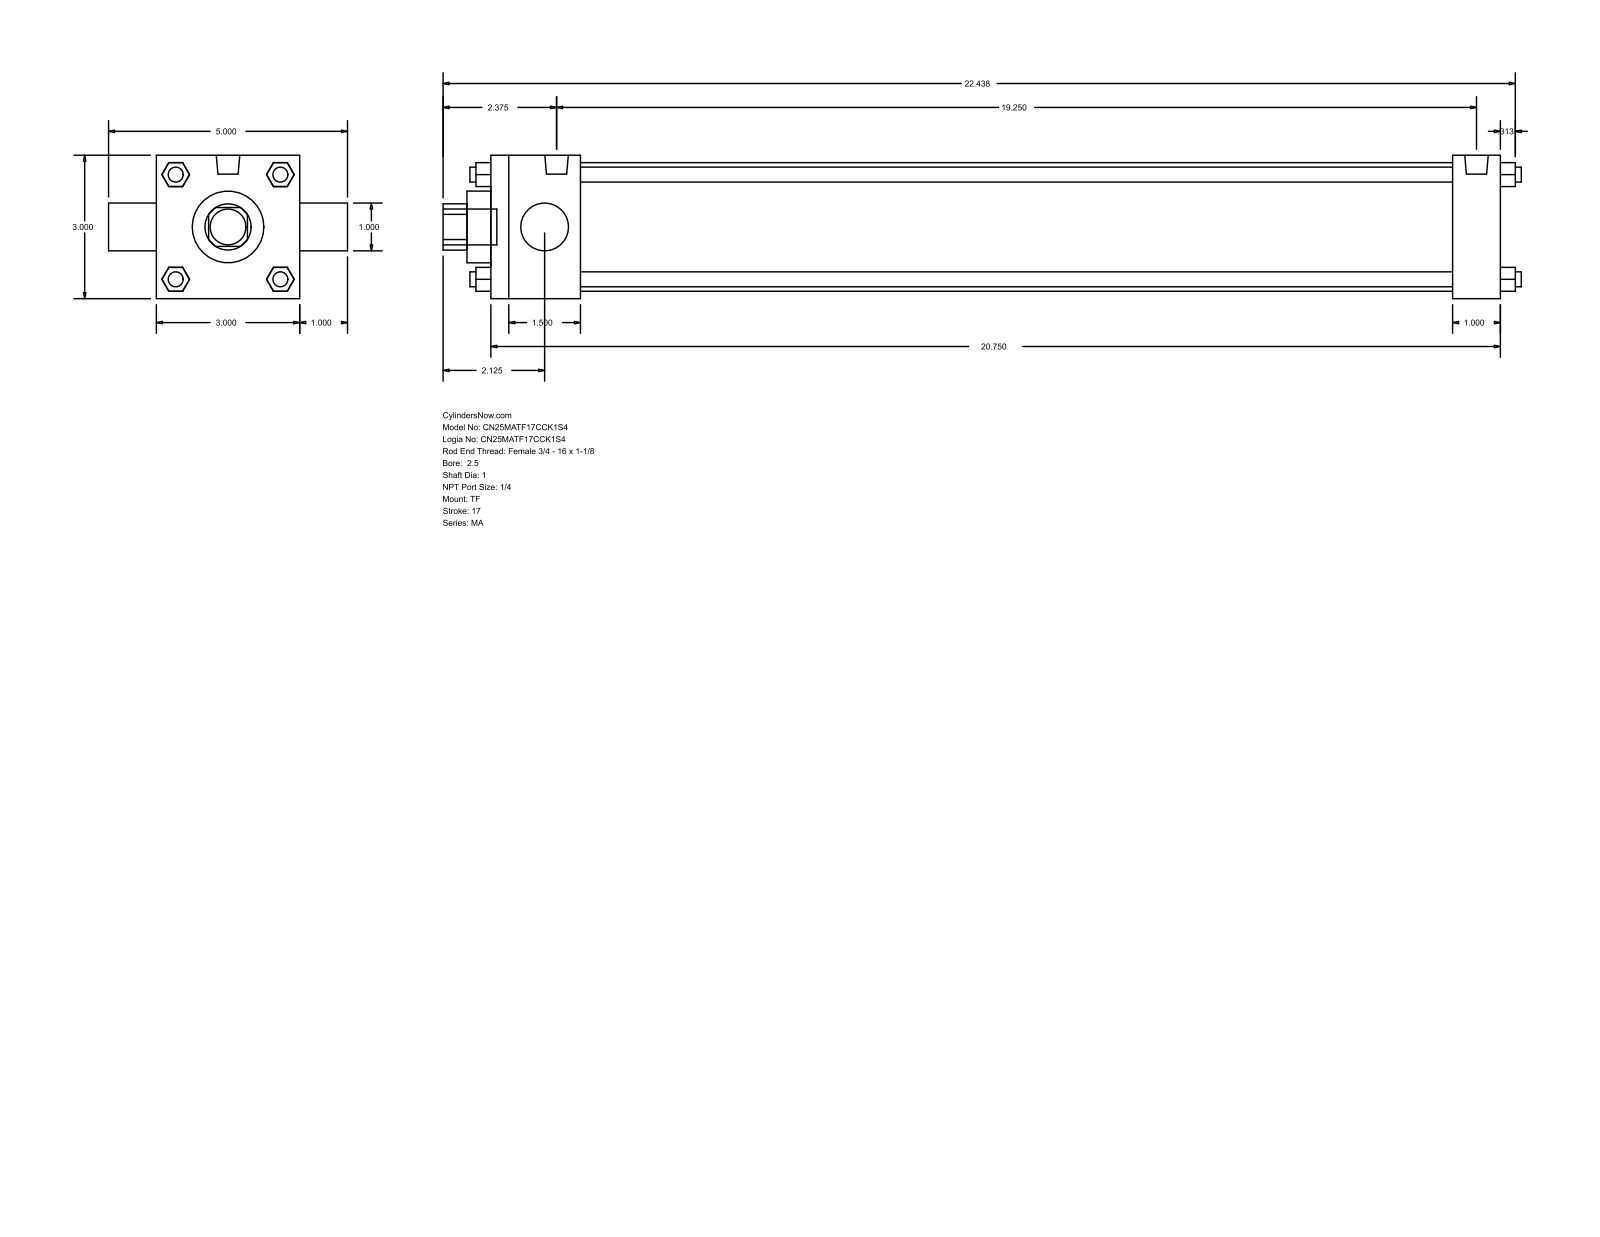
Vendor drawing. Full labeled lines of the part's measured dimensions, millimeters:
Part name (STEP PRODUCT): MA_TF__0250_1
STEP written by: GSSL Pune (CONFIG_CONTROL_DESIGN)
Units: millimetres
Bodies: 0 solids, 120 faces (92 planar, 28 cylindrical, 0 other)
Overall size (bounding box): 573.09 × 127 × 76.2
Round holes (diameter × count): ⌀25.4 ×2, ⌀38.1 ×1, ⌀68.33 ×1
Round bosses / shafts (diameter × count): ⌀7.94 ×7, ⌀12.49 ×2, ⌀19.05 ×1
Partial cylindrical surfaces — rounded edges, fillets, slot ends (radius × count): R12.29 ×1
Main face-to-face distances: 76.2, 536.58, 25.4, 12.7, 47.63, 511.18, 463.55, 488.95, 101.6, 27.81
